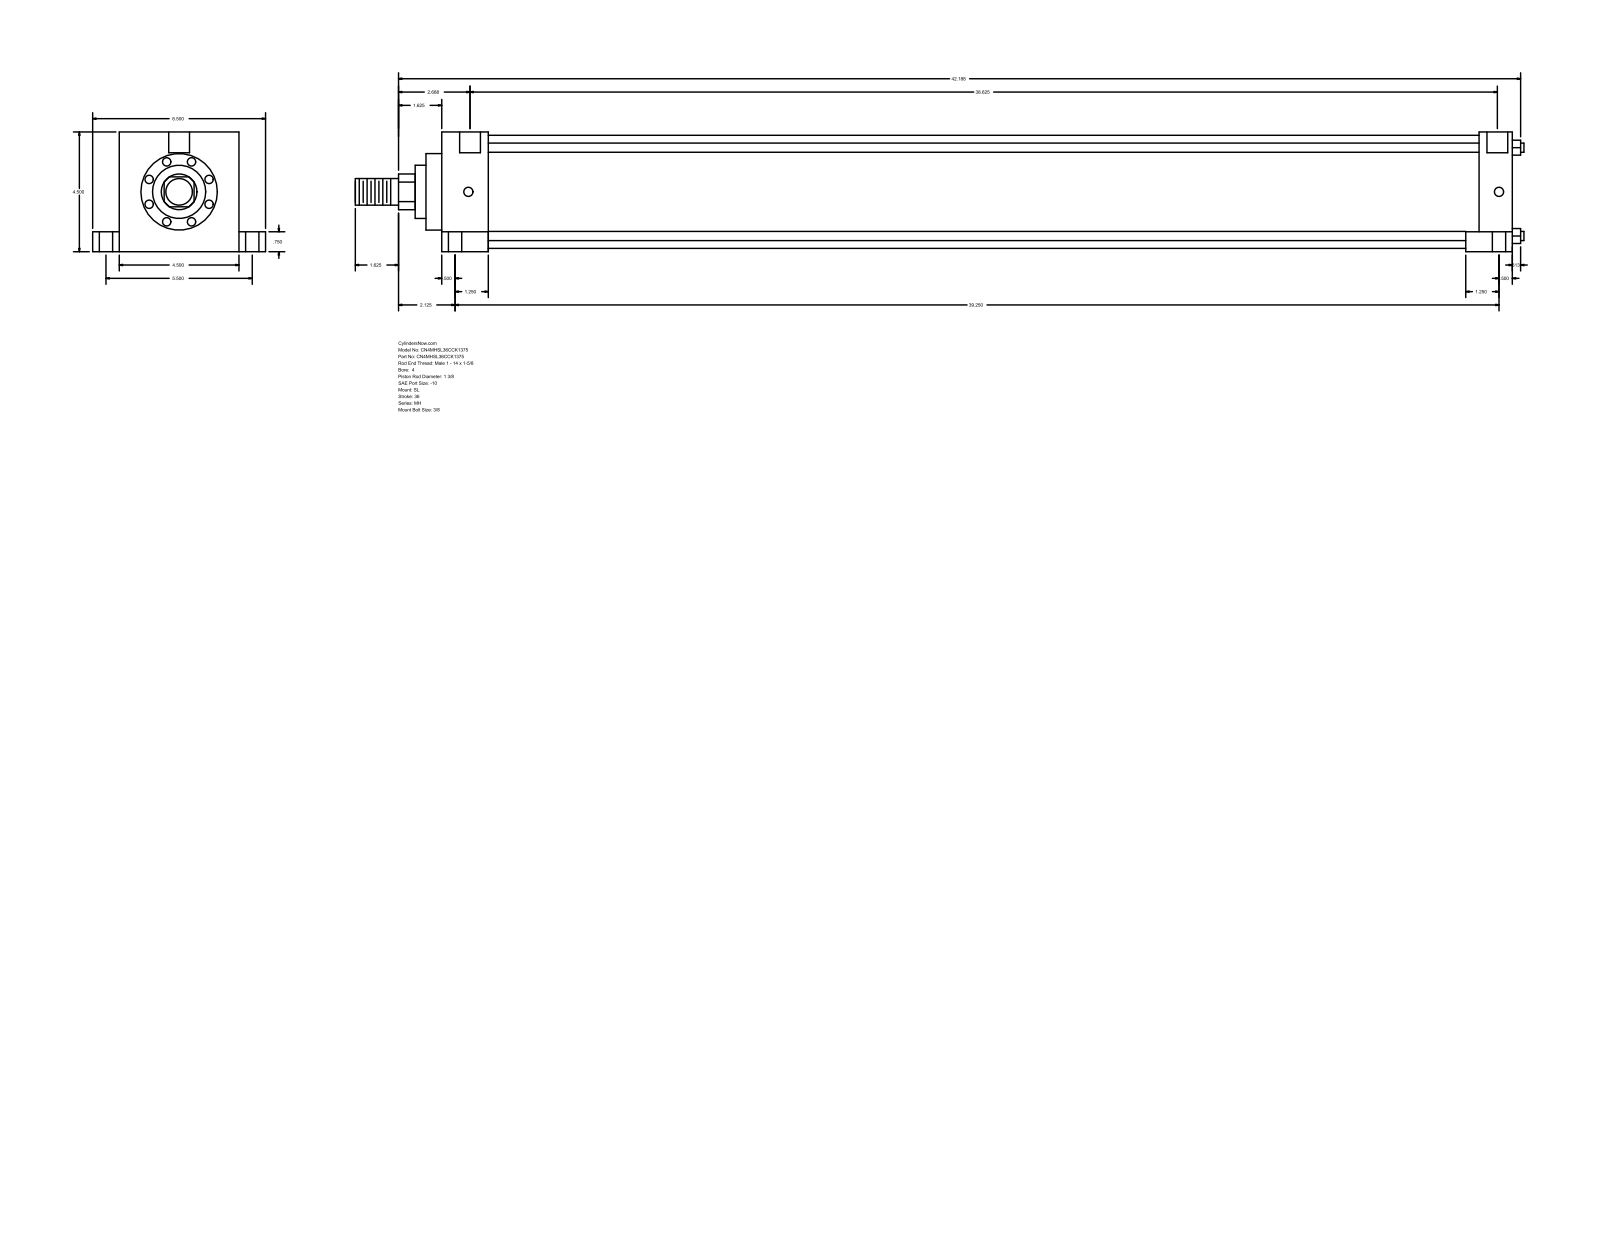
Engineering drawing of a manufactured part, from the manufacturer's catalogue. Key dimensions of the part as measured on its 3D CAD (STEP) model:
Part name (STEP PRODUCT): MH_SL__0400_1.375
STEP written by: GSSL Pune (CONFIG_CONTROL_DESIGN)
Units: millimetres
Bodies: 0 solids, 110 faces (77 planar, 33 cylindrical, 0 other)
Overall size (bounding box): 1116.01 × 165.1 × 114.3
Round holes (diameter × count): ⌀8.73 ×4, ⌀12.7 ×4, ⌀19.05 ×4, ⌀19.84 ×2
Round bosses / shafts (diameter × count): ⌀8.76 ×4, ⌀107.95 ×1, ⌀73.03 ×1, ⌀50.8 ×1, ⌀34.92 ×1, ⌀25.4 ×1
Partial cylindrical surfaces — rounded edges, fillets, slot ends (radius × count): R17.06 ×1
Main face-to-face distances: 114.3, 1022.35, 44.45, 977.9, 990.61, 946.16, 31.74, 25.4, 139.7, 19.05
Hole centre spacings: 69.85, 69.87, 70.99, 71.29, 139.7, 984.25, 985.14, 986.73
